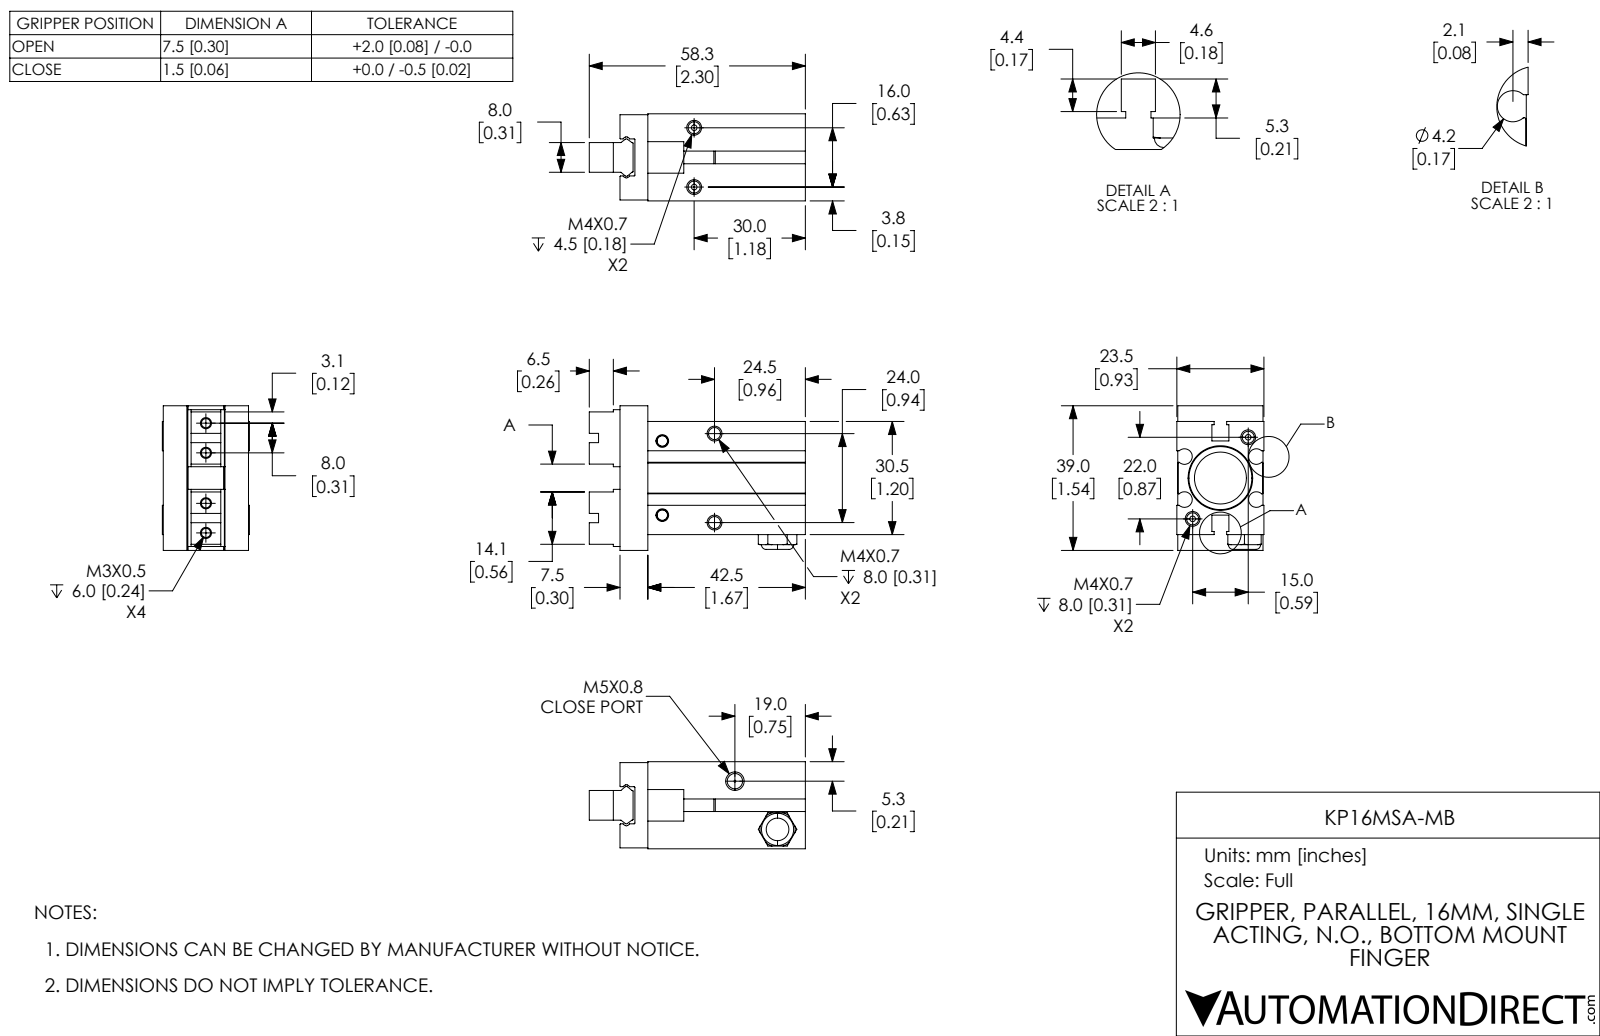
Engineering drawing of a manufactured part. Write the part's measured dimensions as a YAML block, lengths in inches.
part_name: "KP16MSA-MB; KP16MSA-MB-3; KP16MSA-MB-2; KP16MSA-MB-1"
step_written_by: "SolidWorks 2017 (CONFIG_CONTROL_DESIGN)"
units: inches
bodies: {solids: 3, faces: 263, planar: 133, cylindrical: 68, other: 62}
overall_size: [2.295, 1.535, 0.925]
volume: 1.861
surface_area: 20.86
round_holes:
  - {diameter: 0.128, count: 6}
  - {diameter: 0.02, count: 2}
  - {diameter: 0.097, count: 2}
  - {diameter: 0.158, count: 2}
  - {diameter: 0.163, count: 2}
  - {diameter: 0.24, count: 1}
  - {diameter: 0.551, count: 1}
  - {diameter: 0.669, count: 1}
partial_cylinders:
  - {radius: 0.008, count: 10}
  - {radius: 0.083, count: 4}
  - {radius: 0.016, count: 2}
  - {radius: 0.02, count: 2}
  - {radius: 0.039, count: 2}
  - {radius: 0.048, count: 2}
  - {radius: 0.048, count: 2}
face_to_face_distances: [0.295, 0.62, 0.157, 1.201, 0.915, 0.913, 0.541, 0.925, 0.283, 0.138]
hole_center_spacings: [0.268, 0.339, 0.524, 0.761, 0.437, 0.535, 0.63, 0.683]
